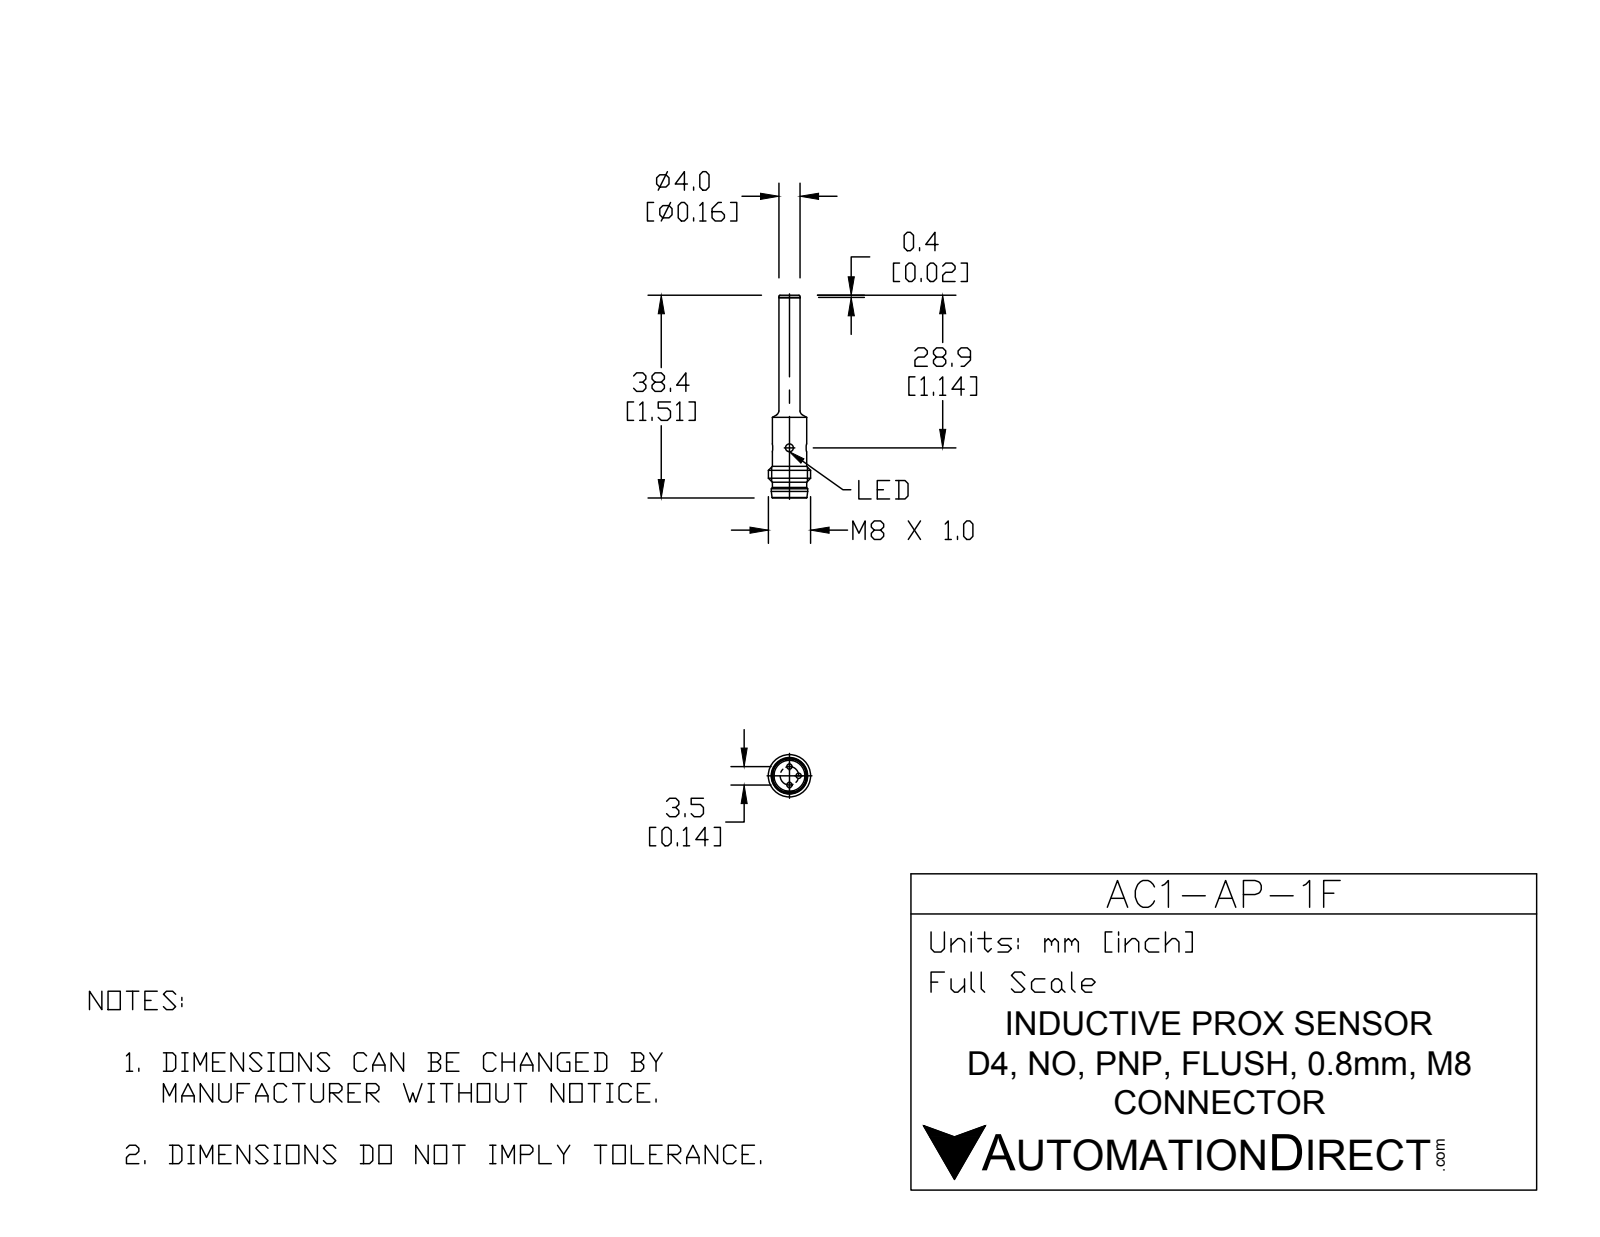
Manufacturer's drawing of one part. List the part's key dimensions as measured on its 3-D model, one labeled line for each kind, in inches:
Part name (STEP PRODUCT): AC1-AP-1F
STEP written by: SolidWorks 2015 (CONFIG_CONTROL_DESIGN)
Units: inches
Bodies: 4 solids, 59 faces (11 planar, 26 cylindrical, 22 other)
Overall size (bounding box): 1.512 × 0.315 × 0.315
Volume: 0.046 in³ · Surface area: 1.3 in²
Round holes (diameter × count): ⌀0.059 ×2, ⌀0.23 ×1
Round bosses / shafts (diameter × count): ⌀0.039 ×3, ⌀0.315 ×1, ⌀0.272 ×1, ⌀0.256 ×1, ⌀0.157 ×1
Main face-to-face distances: 1.315, 0.217, 0.197, 1.512, 1.496, 1.299, 0.016
